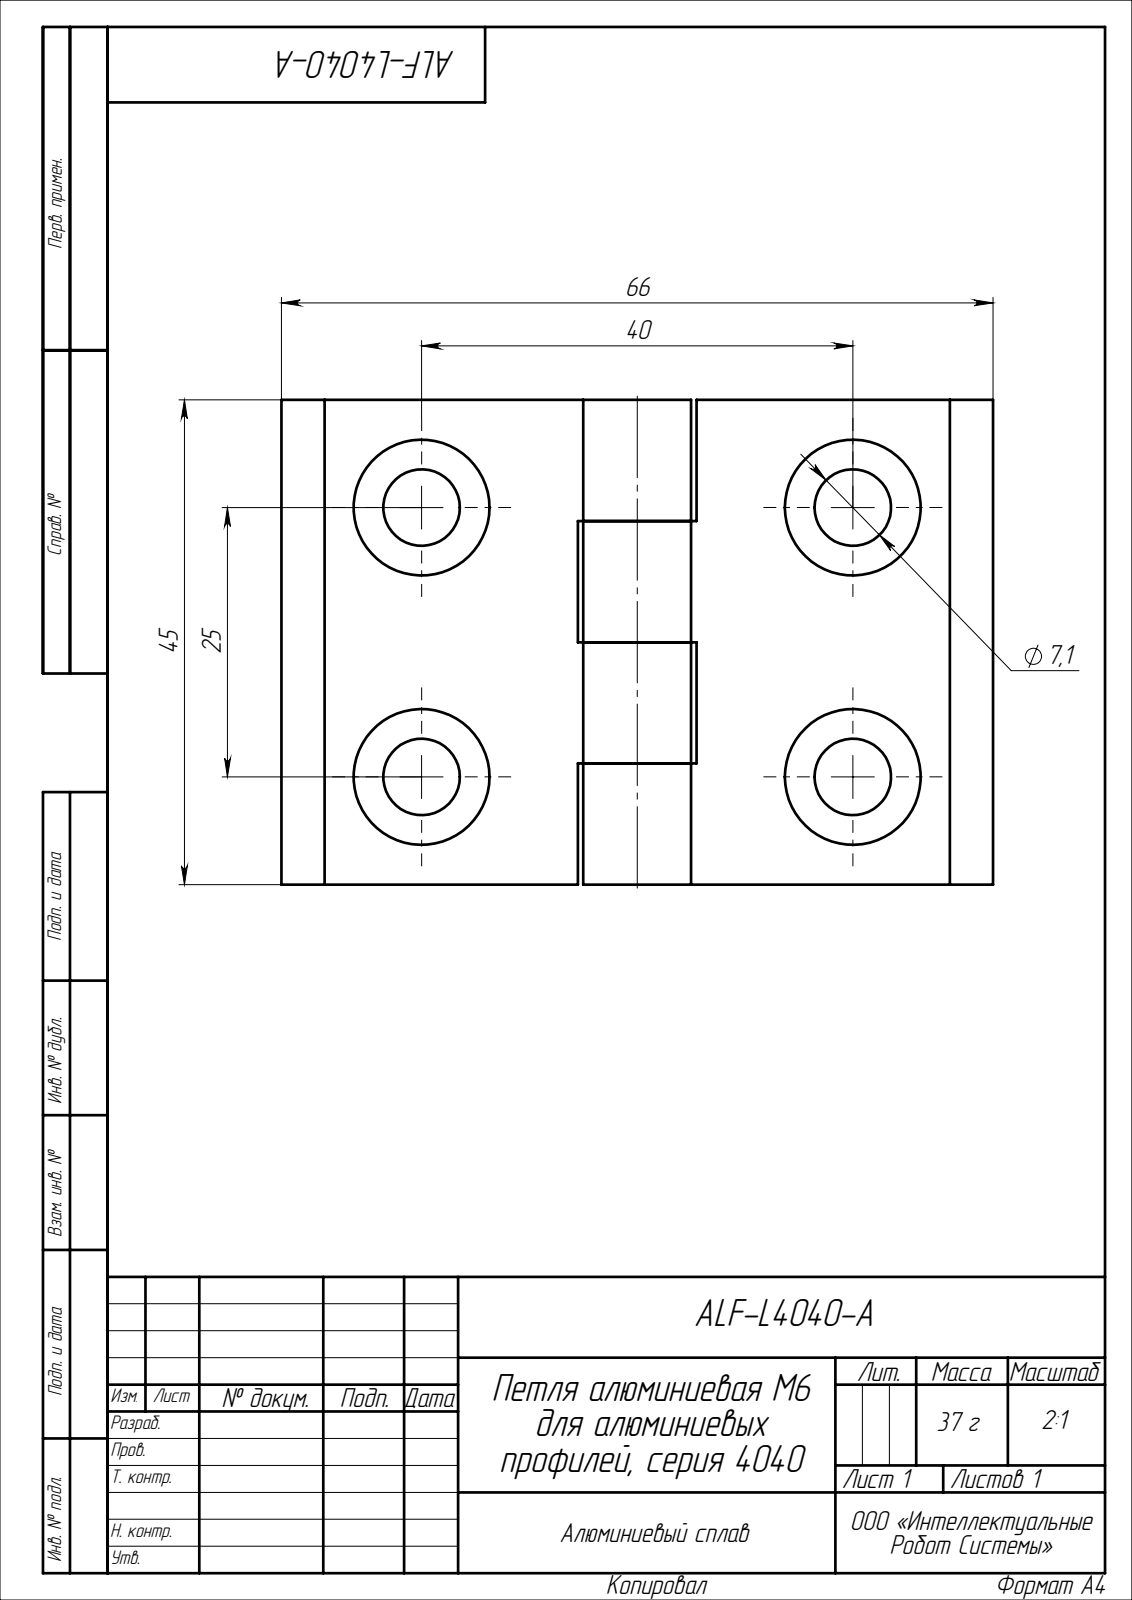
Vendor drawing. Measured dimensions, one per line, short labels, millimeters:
name: ALF-L4040-A
written by: SolidWorks 2022 (CONFIG_CONTROL_DESIGN)
unit: mm
bodies: 2 solids, 50 faces (22 planar, 20 cylindrical, 8 other)
size: 66 × 45 × 10
volume: 14 157 mm³; area: 8 013 mm²
holes: 4× ⌀7.1, 4× ⌀12.6
bosses: 1× ⌀10
face distances: 5, 11.25, 22.5, 33.75, 45, 11, 27.5, 38.5, 66
hole spacings: 25, 40, 47.17
